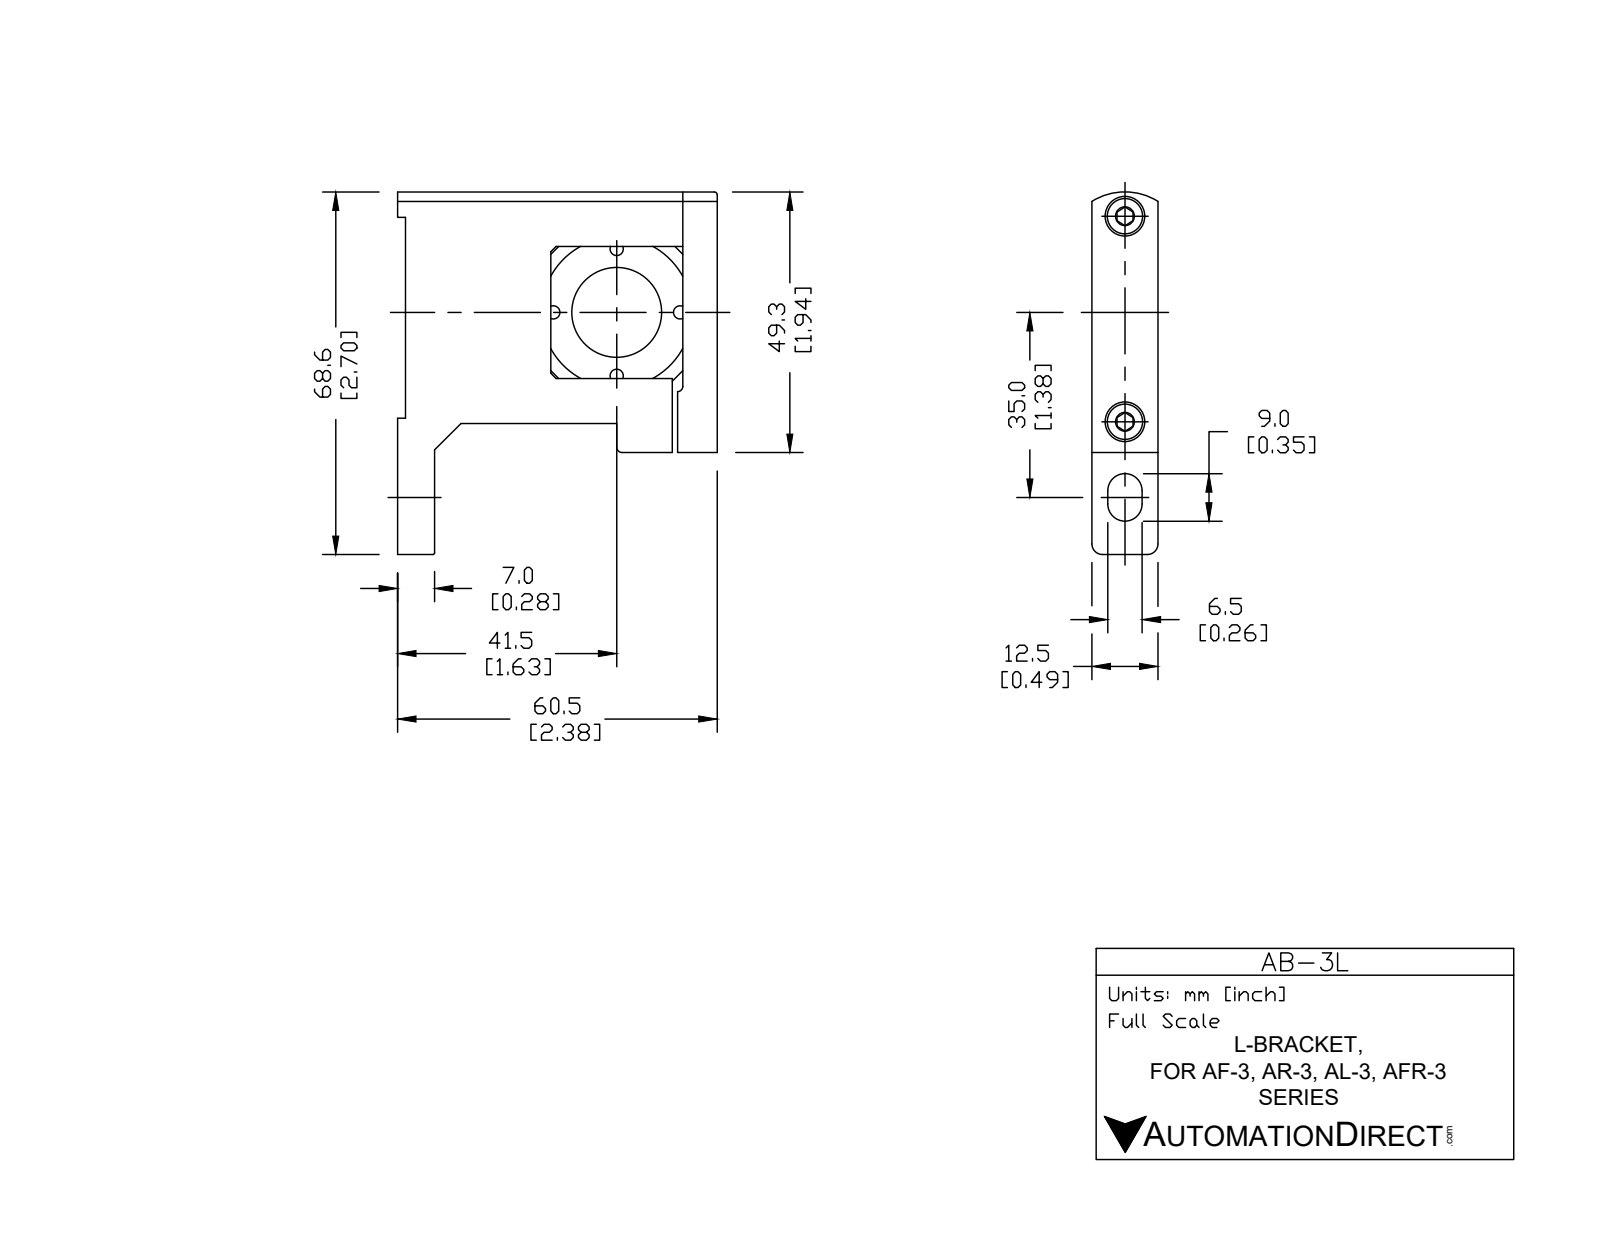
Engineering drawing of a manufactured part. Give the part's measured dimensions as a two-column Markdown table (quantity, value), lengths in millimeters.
| quantity | value |
| --- | --- |
| part name | AB-3L |
| STEP written by | SolidWorks 2015 (CONFIG_CONTROL_DESIGN) |
| units | millimeters |
| bodies | 3 solids, 103 faces (69 planar, 22 cylindrical, 12 other) |
| overall size | 66.8 × 60.5 × 12.5 |
| volume | 26 826 mm³ |
| surface area | 11 692 mm² |
| round holes (diameter × count) | 4.5 × 2, 6.21 × 2, 17 × 1 |
| round bosses / shafts (diameter × count) | 5.75 × 2, 4 × 2 |
| partial cylindrical surfaces (radius × count) | 3.25 × 2, 1.5 × 1, 11.75 × 1 |
| main face-to-face distances | 12.5, 2, 27, 29, 6.5, 59.25, 10.5, 5.81, 6.69, 3.81 |
| hole center spacings | 38.9 |
